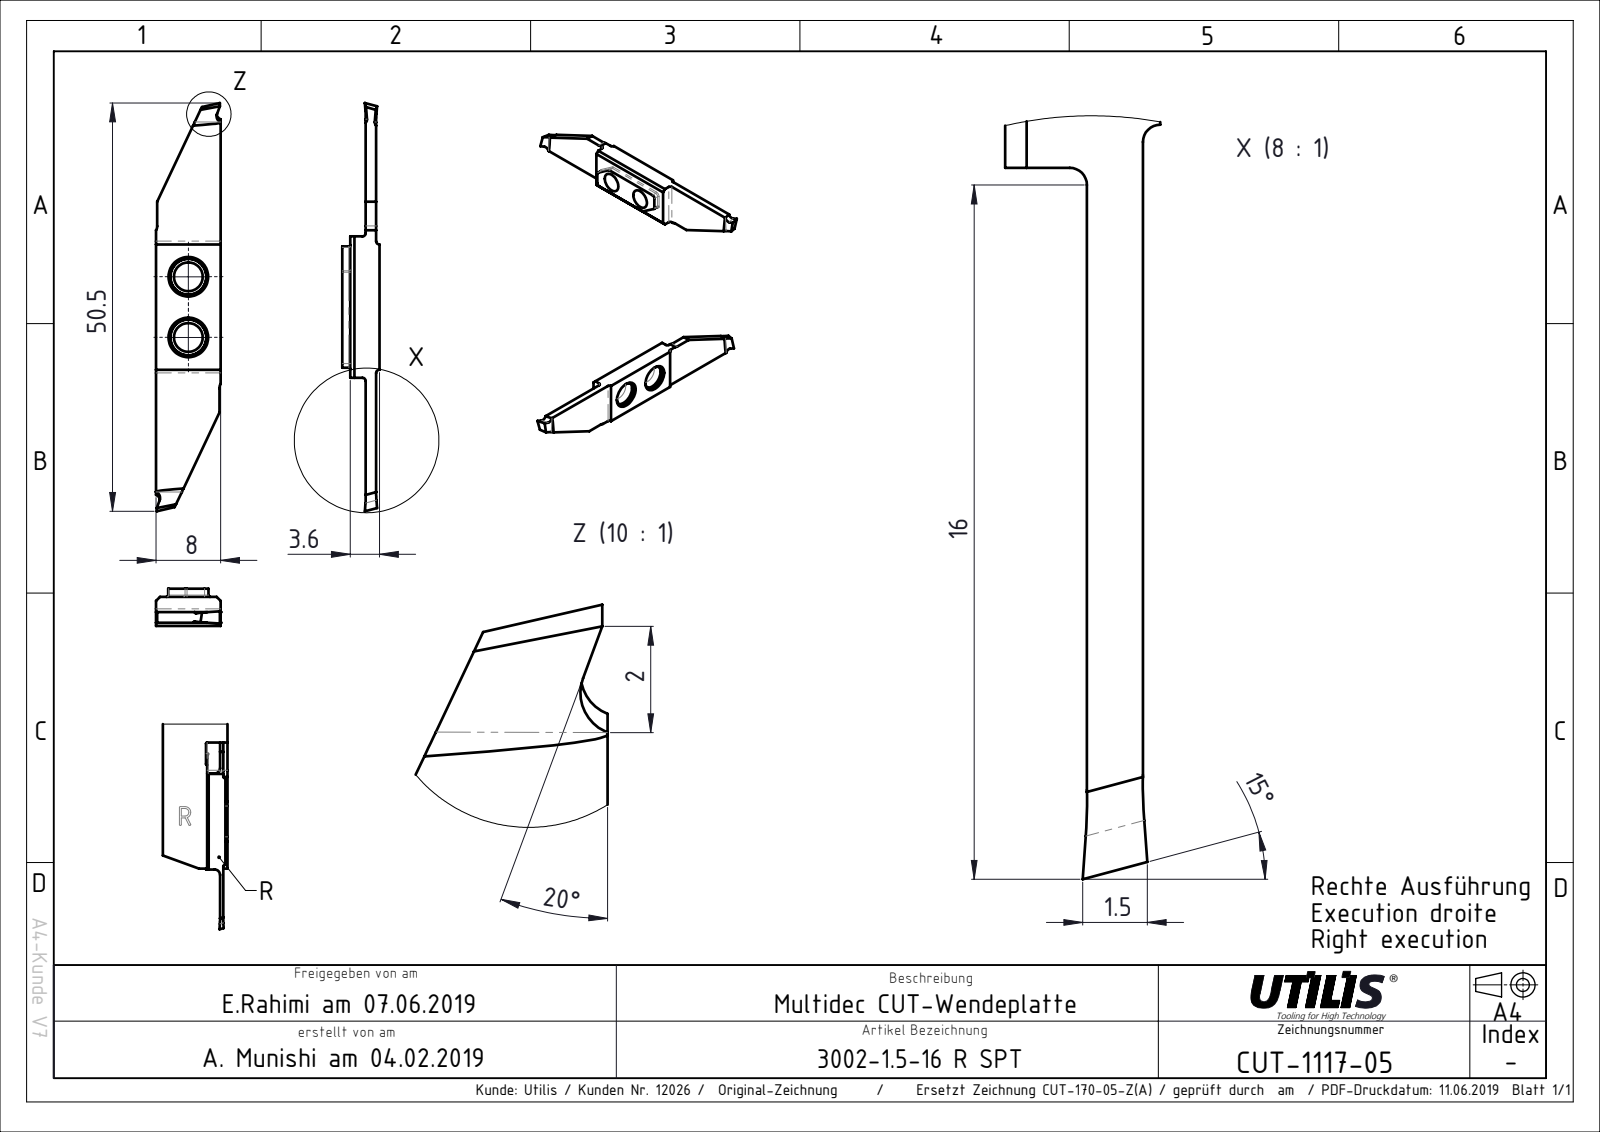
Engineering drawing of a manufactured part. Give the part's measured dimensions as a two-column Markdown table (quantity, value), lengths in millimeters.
| quantity | value |
| --- | --- |
| part name | CUT-1117; ASME Y14.5 |
| STEP written by | FormatWorks Professional (AP242_MANAGED_MODEL_BASED_3D_ENGINEERING_MIM_LF) |
| units | millimeters |
| bodies | 1 solid, 34 faces (24 planar, 10 cylindrical, 0 other) |
| overall size | 50.5 × 8 × 3.6 |
| volume | 666 mm³ |
| surface area | 937 mm² |
| round holes (diameter × count) | 3.55 × 2 |
| partial cylindrical surfaces (radius × count) | 0.4 × 4, 1 × 2 |
| main face-to-face distances | 1.28, 1.69, 0.41, 1.91, 3.19, 3.6, 8, 18.09, 17.5, 7.85 |
| hole center spacings | 7.5 |
